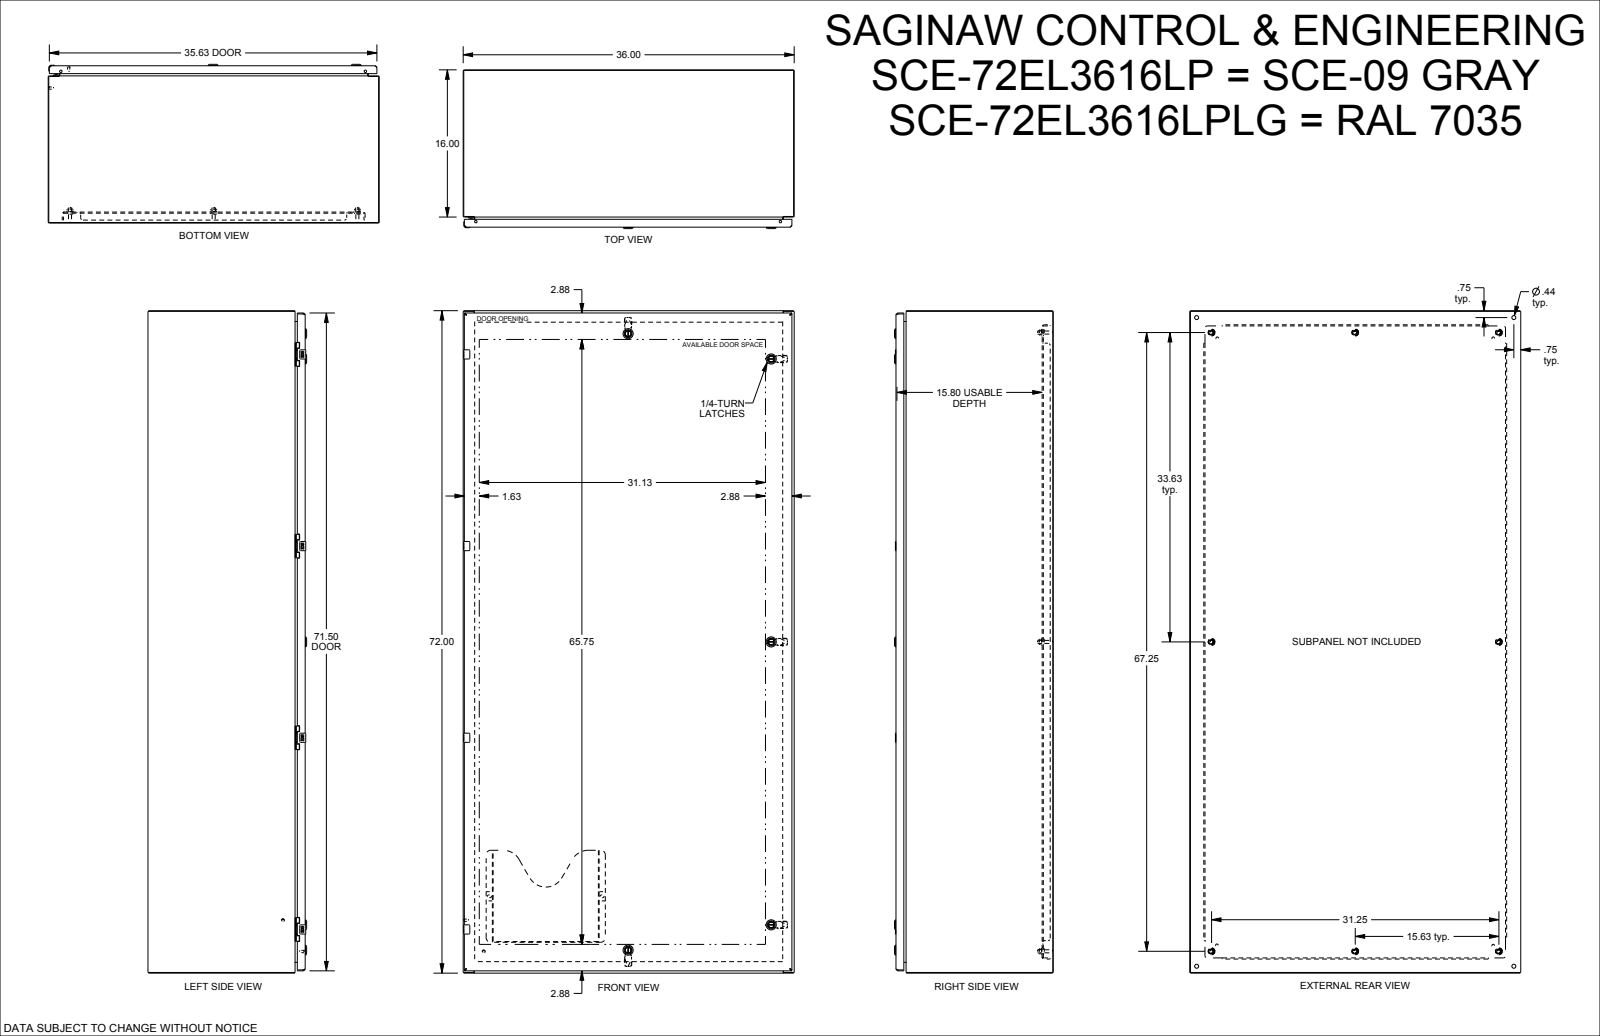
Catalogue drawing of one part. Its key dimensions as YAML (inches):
part_name: "SCE-72EL3616LP"
step_written_by: "SolidWorks 2019 (CONFIG_CONTROL_DESIGN)"
units: inches
bodies: {solids: 0, faces: 5207, planar: 2557, cylindrical: 1466, other: 1184}
overall_size: [72, 36, 17.256]
round_holes:
  - {diameter: 0.172, count: 8}
  - {diameter: 0.205, count: 8}
  - {diameter: 0.244, count: 8}
  - {diameter: 0.266, count: 8}
  - {diameter: 0.367, count: 8}
  - {diameter: 0.375, count: 8}
  - {diameter: 0.5, count: 8}
  - {diameter: 0.197, count: 5}
  - {diameter: 0.315, count: 5}
  - {diameter: 0.394, count: 5}
  - {diameter: 0.634, count: 5}
  - {diameter: 0.04, count: 4}
round_bosses_or_shafts:
  - {diameter: 0.17, count: 12}
  - {diameter: 0.366, count: 8}
  - {diameter: 0.332, count: 8}
  - {diameter: 0.25, count: 8}
  - {diameter: 0.24, count: 8}
  - {diameter: 1.102, count: 5}
  - {diameter: 0.866, count: 5}
  - {diameter: 0.802, count: 5}
partial_cylinders:
  - {radius: 0.012, count: 136}
  - {radius: 0.01, count: 52}
  - {radius: 0.02, count: 52}
  - {radius: 0.015, count: 40}
  - {radius: 0.03, count: 25}
  - {radius: 0.025, count: 20}
  - {radius: 0.1, count: 20}
  - {radius: 0.157, count: 20}
face_to_face_distances: [0.075, 0.104, 16.995, 16.92, 17.099, 17.024, 0.075, 1.125, 15.795, 1]
hole_center_spacings: [20.833, 41.667, 20.833, 62.5, 0.493, 0.05, 0.494, 0.986]
